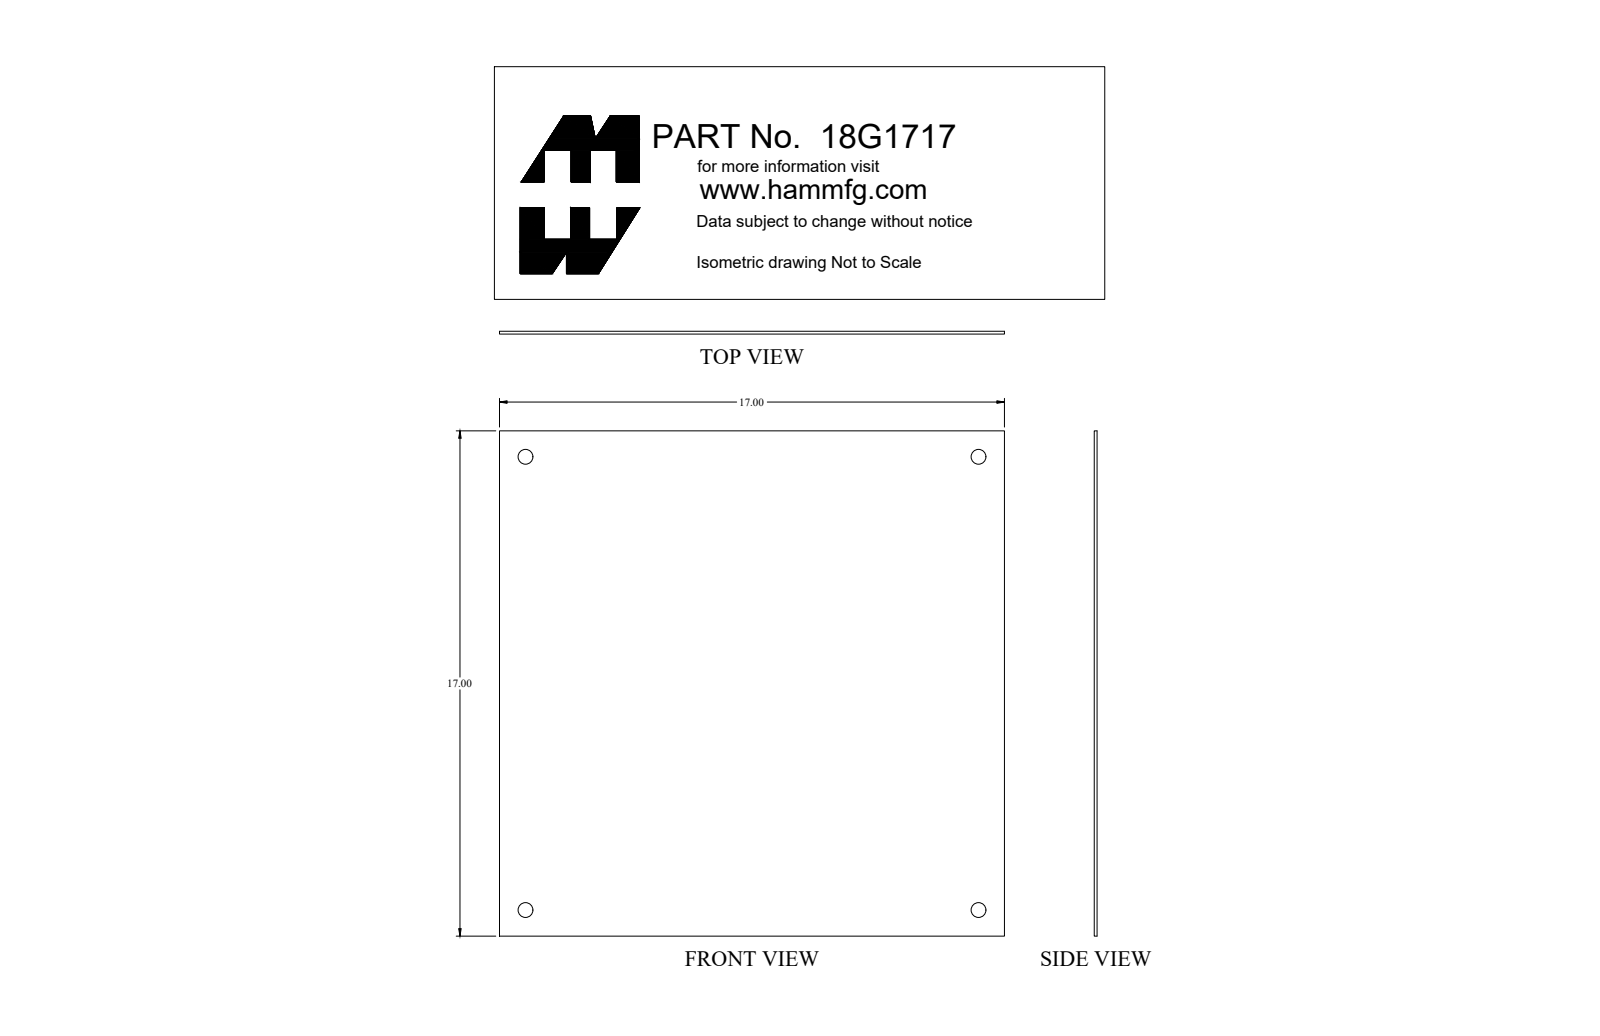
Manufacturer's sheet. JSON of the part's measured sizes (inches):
{"part_name": "18G1717", "step_written_by": "SolidWorks 2018 (AUTOMOTIVE_DESIGN)", "units": "inches", "bodies": {"solids": 1, "faces": 10, "planar": 6, "cylindrical": 4, "other": 0}, "overall_size": [17, 17, 0.095], "volume_in3": 27.38, "surface_area_in2": 583.5, "round_holes": [[0.5, 4]], "face_to_face_distances": [0.095, 17], "hole_center_spacings": [15.25, 21.566]}
